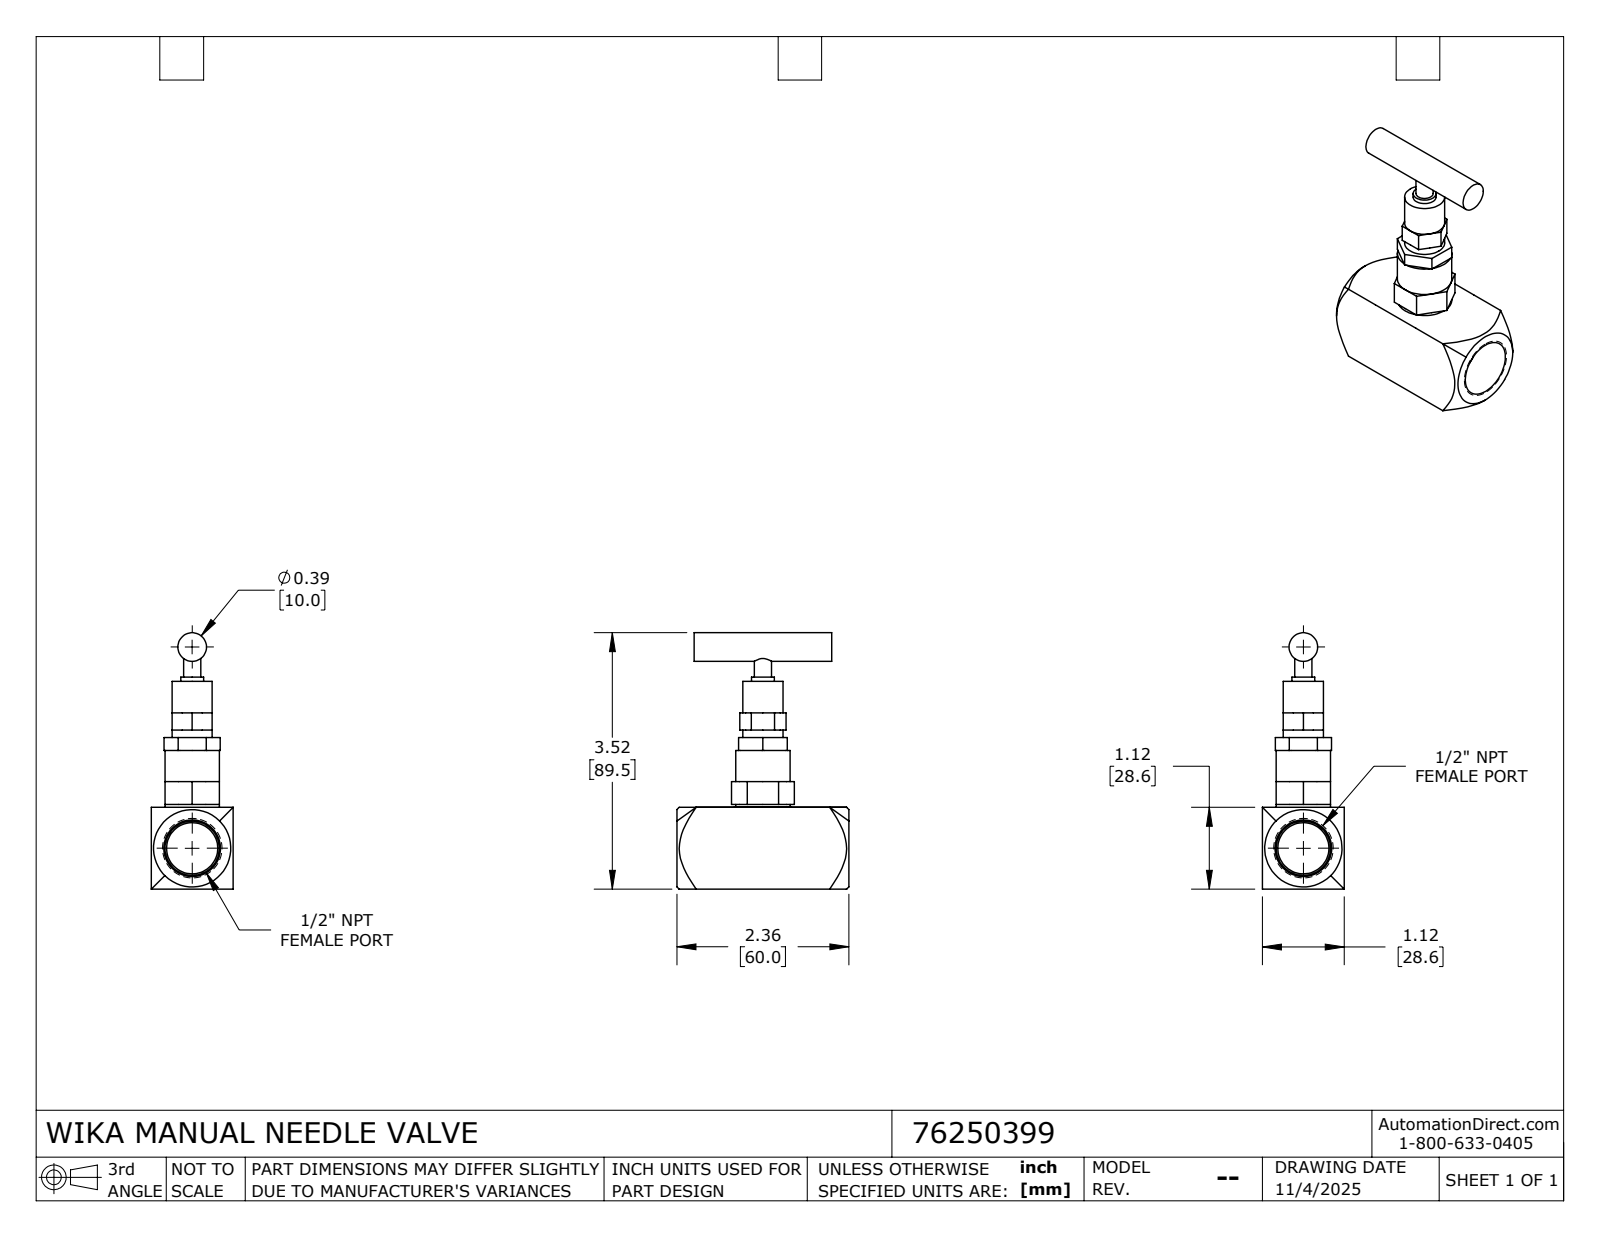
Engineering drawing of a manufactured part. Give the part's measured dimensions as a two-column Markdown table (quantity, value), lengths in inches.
| quantity | value |
| --- | --- |
| part name | 76250399 |
| STEP written by | SolidWorks 2024 (CONFIG_CONTROL_DESIGN) |
| units | inches |
| bodies | 2 solids, 87 faces (59 planar, 20 cylindrical, 8 other) |
| overall size | 3.525 × 2.362 × 1.125 |
| volume | 3.107 in³ |
| surface area | 23.53 in² |
| round holes (diameter × count) | 0.703 × 1 |
| round bosses / shafts (diameter × count) | 0.748 × 1, 0.551 × 1, 0.394 × 1, 0.315 × 1, 0.236 × 1 |
| main face-to-face distances | 1.125, 1.125, 0.787, 1.575, 0.551, 0.098, 0.65, 2.362, 0.748, 1.907 |
